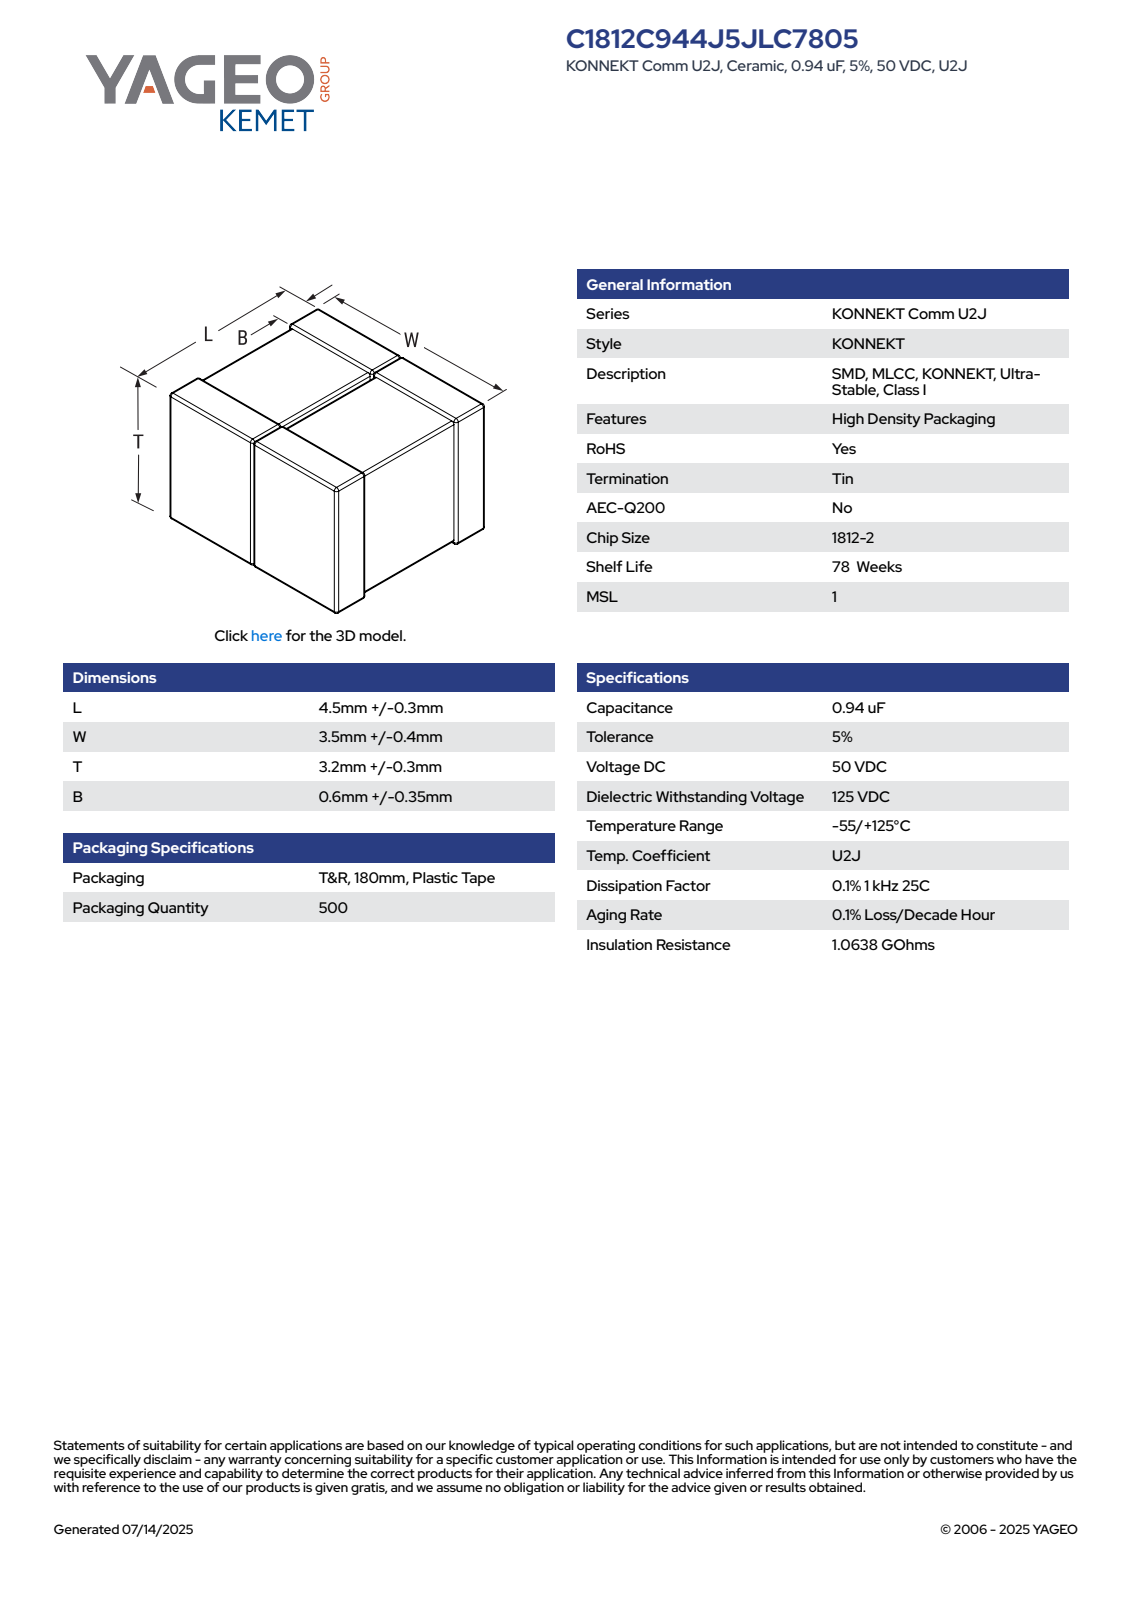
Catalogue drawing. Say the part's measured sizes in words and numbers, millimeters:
The part is named "CCSS_K2LL_1812-2_L4.8W3.9B0.95T3.5". Its 3-D file was written by "SolidWorks 2021 (AUTOMOTIVE_DESIGN)". It is 8 solids with 234 faces: 142 planar, 60 cylindrical and 32 other. Overall it measures 4.8 by 3.9 by 3.5 millimeters. Its volume is 61 cubic millimeters and its surface area 130 square millimeters. The main face-to-face distances are 1.88, 1.95, 1.81, 4.8, 3.43, 2.02, 3.83, 3.36, 3.76, 3.5.
